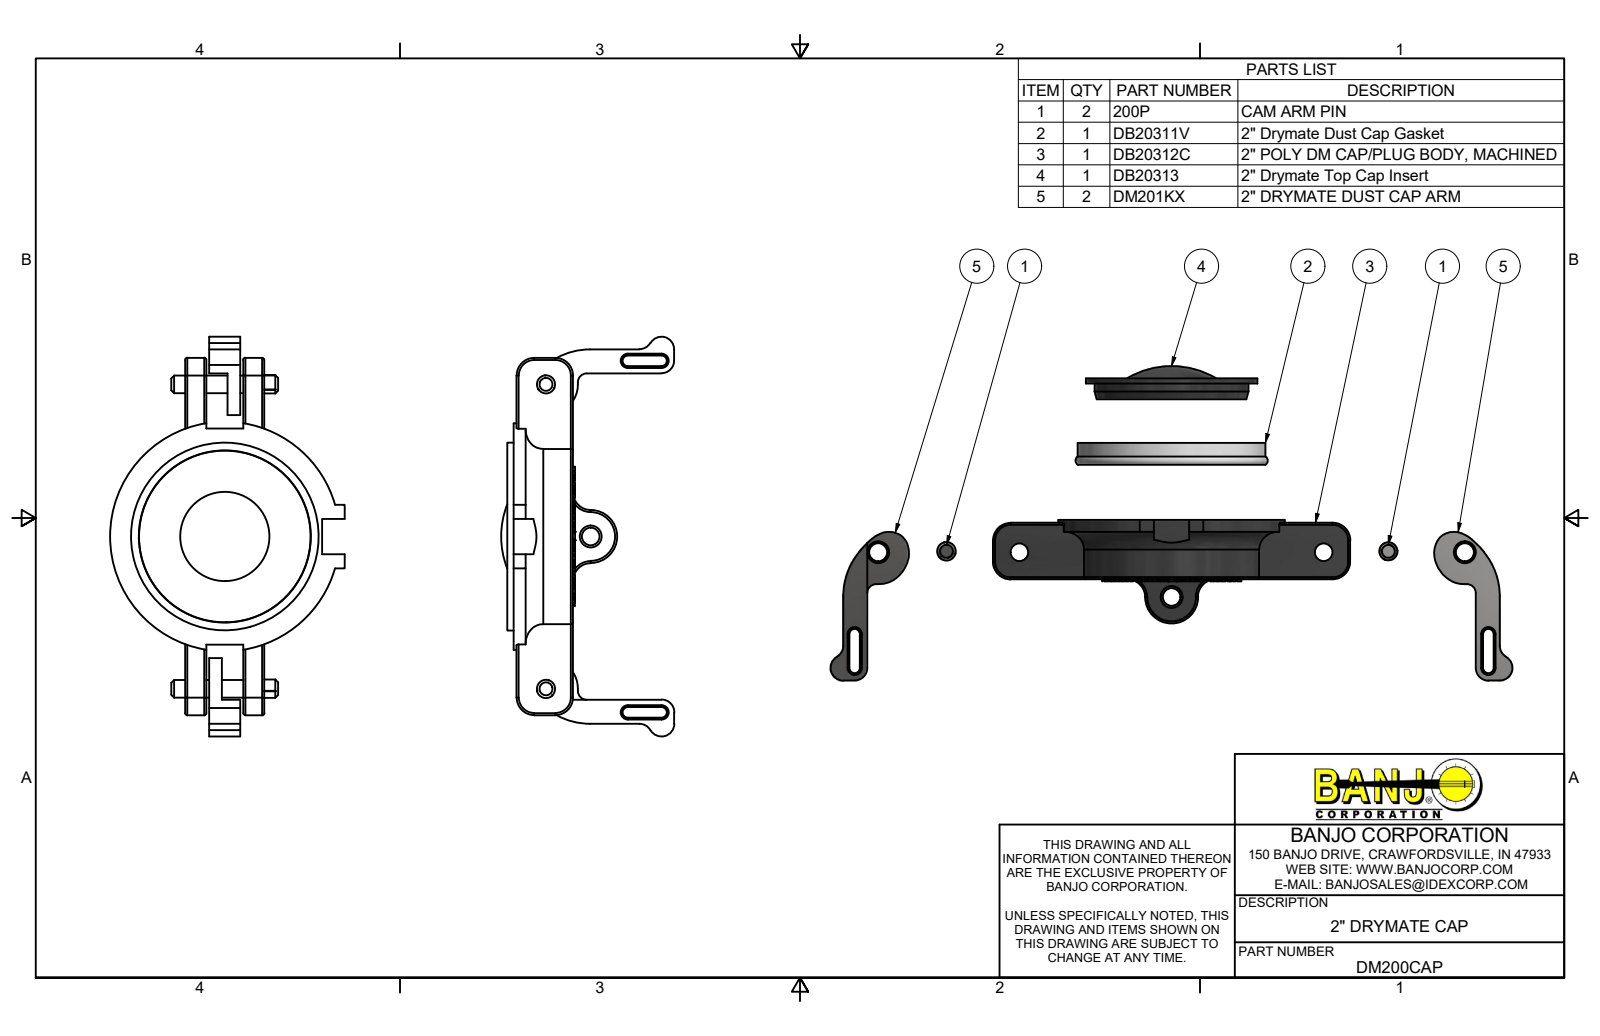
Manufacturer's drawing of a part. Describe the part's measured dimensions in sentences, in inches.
The part is named "DM200CAP; DB20312C; DB20312AX; DB20311V (+3 more)". Its 3-D file was written by "Autodesk Inventor 2019 (AUTOMOTIVE_DESIGN)". It is 7 solids with 671 faces: 382 planar, 104 cylindrical and 185 other. Overall it measures 5.66 by 3.325 by 2.451 inches. Its volume is 6.14 cubic inches and its surface area 74.07 square inches. Round holes: 3 of diameter 0.125, 3 of diameter 0.25, 2 of diameter 0.256, 1 of diameter 2.188, 1 of diameter 2.438, 1 of diameter 2.655. Round bosses or shafts: 3 of diameter 0.28, 2 of diameter 0.26, 2 of diameter 0.249, 1 of diameter 3.25, 1 of diameter 2.72, 1 of diameter 2.66, 1 of diameter 2.43, 1 of diameter 2.18. Partial cylindrical surfaces (rounded edges, fillets, slot ends): 20 of radius 0.03, 6 of radius 0.18, 6 of radius 0.25, 4 of radius 0.075, 2 of radius 0.124, 2 of radius 0.983, 1 of radius 0.375, 1 of radius 1.045. The main face-to-face distances are 0.298, 0.822, 0.78, 0.225, 0.62, 0.845, 0.22, 0.84, 0.34, 0.042. The hole center spacings are 0.95, 1.645, 2.246, 1.646, 4.31.
